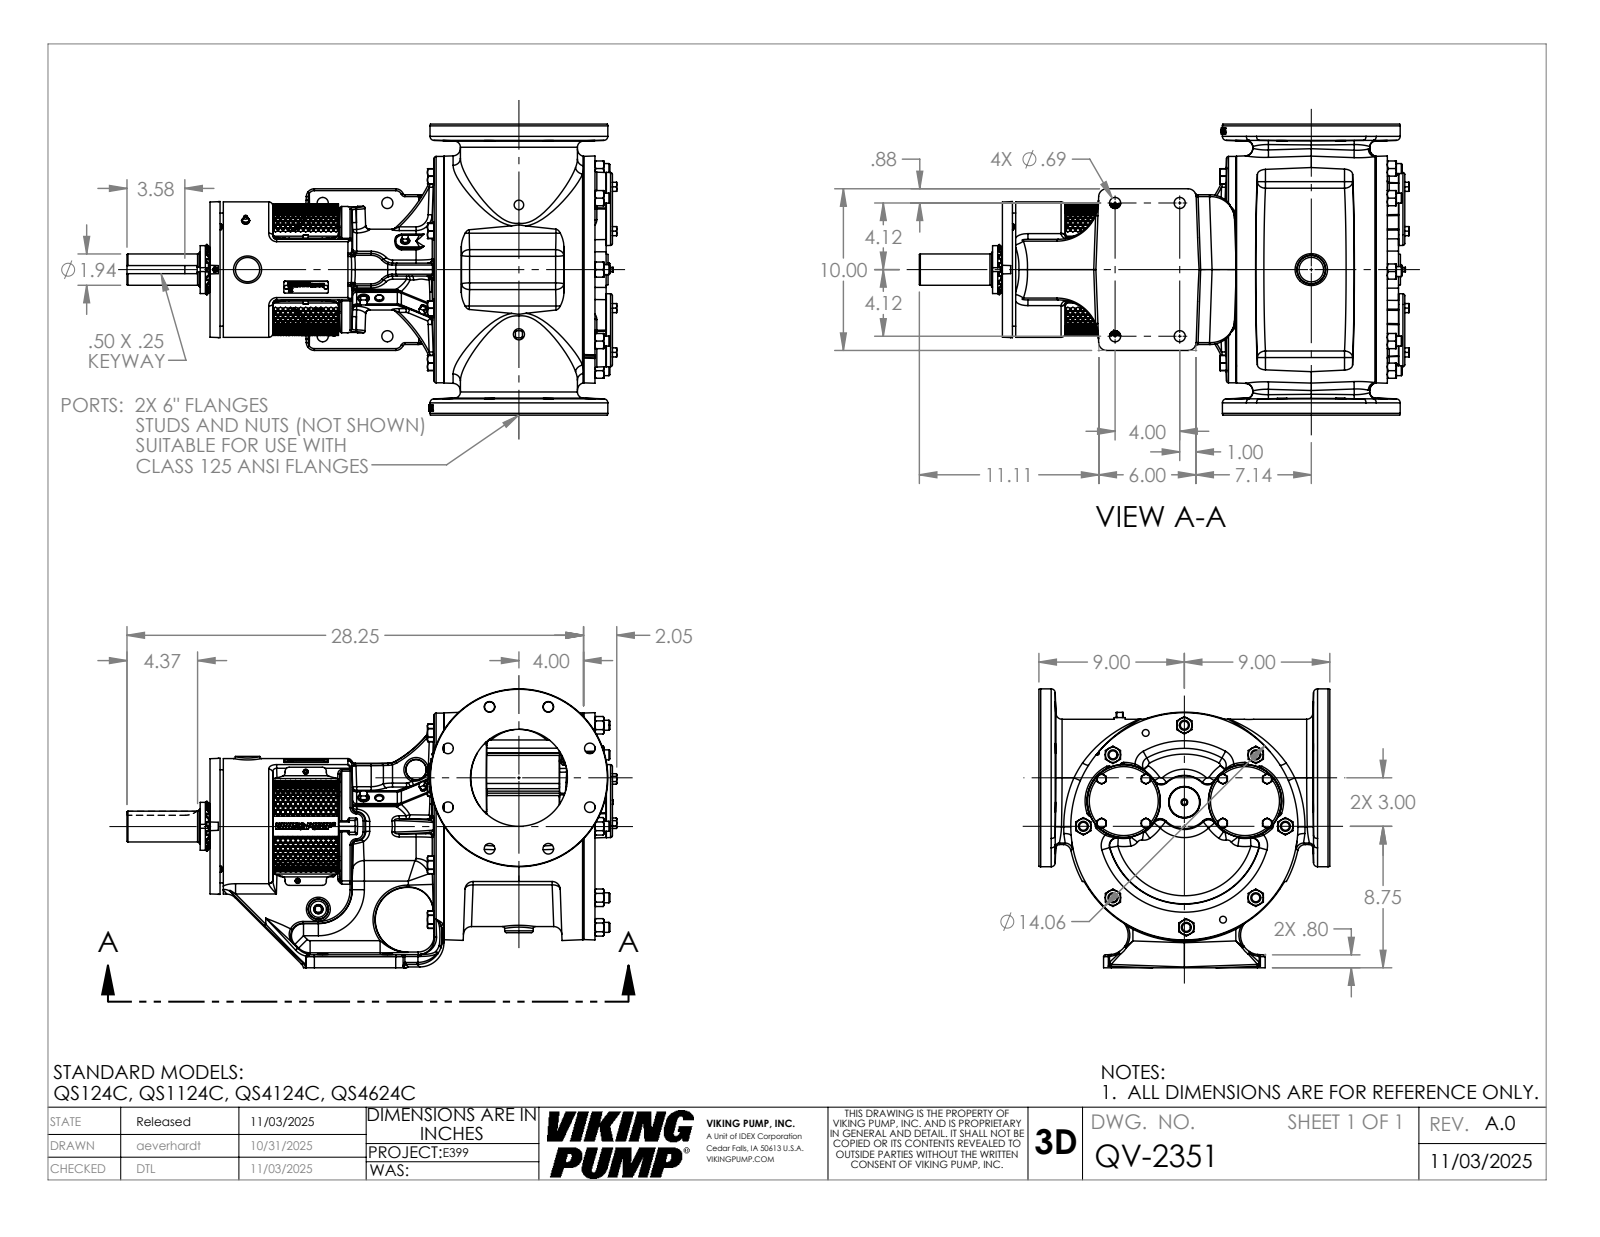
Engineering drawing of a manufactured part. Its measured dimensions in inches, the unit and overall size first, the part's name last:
Units: inches
Overall size (bounding box): 30.304 × 22.74 × 17.25
Round holes (diameter × count): ⌀0.266 ×8, ⌀0.656 ×8, ⌀1.157 ×8, ⌀0.25 ×6, ⌀0.688 ×4, ⌀0.159 ×2, ⌀0.313 ×2, ⌀0.422 ×2, ⌀0.453 ×1, ⌀2.157 ×1, ⌀2.167 ×1, ⌀2.182 ×1
Round bosses / shafts (diameter × count): ⌀0.75 ×8, ⌀0.742 ×8, ⌀0.617 ×8, ⌀0.437 ×3, ⌀0.312 ×3, ⌀4.5 ×2, ⌀0.375 ×2, ⌀14 ×1
Partial cylindrical surfaces — rounded edges, fillets, slot ends (radius × count): R0.12 ×60, R0.5 ×23, R0.25 ×22, R0.015 ×18, R0.092 ×18, R0.07 ×16, R0.75 ×14, R0.06 ×8
Main face-to-face distances: 18, 1.5, 23.817, 16.5, 3.82, 19.998, 17, 15.5, 1, 24.898
Hole centre spacings: 3.75, 2.079, 5.783, 2.713, 3.133, 3.788, 5.423, 5.932
Volume: 2 360 in³ · Surface area: 2 391 in²
Bodies: 1 solid, 4168 faces (1421 planar, 688 cylindrical, 2059 other)
Part name (STEP PRODUCT): QV-2351
STEP written by: SolidWorks 2024 (AUTOMOTIVE_DESIGN)
